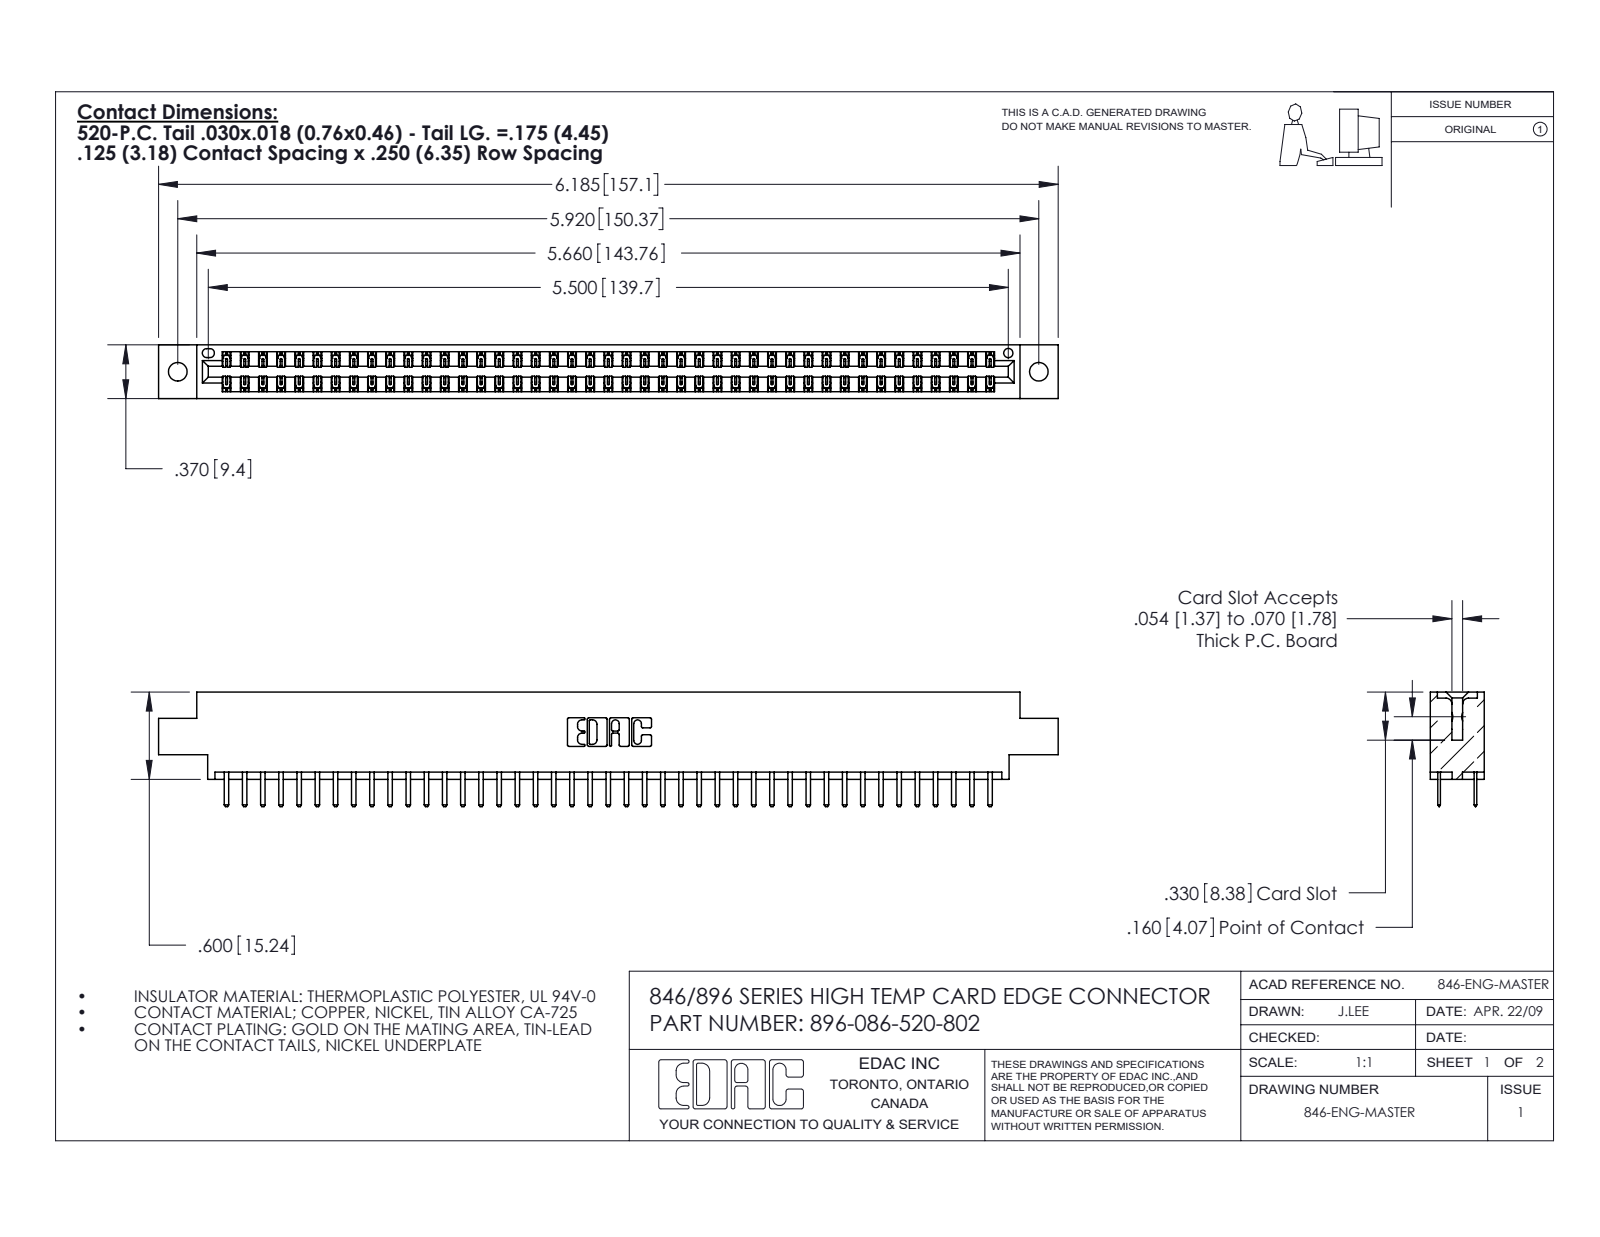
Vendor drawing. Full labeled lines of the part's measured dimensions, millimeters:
Part name (STEP PRODUCT): 345-292-001_345-293-120; 346 Part_0.170 Offset - 0.128 Dia; 396-086-520-802
STEP written by: SolidWorks 2016 (CONFIG_CONTROL_DESIGN)
Units: millimetres
Bodies: 87 solids, 4942 faces (3262 planar, 1680 cylindrical, 0 other)
Overall size (bounding box): 157.1 × 20 × 9.4
Volume: 15 100 mm³ · Surface area: 20 590 mm²
Round holes (diameter × count): ⌀3.3 ×2, ⌀1.6 ×1
Partial cylindrical surfaces — rounded edges, fillets, slot ends (radius × count): R0.2 ×129, R0.3 ×90, R0.3 ×22, R0.2 ×6, R0.8 ×6, R0.7 ×3, R0.4 ×2, R0.6 ×2
Main face-to-face distances: 1.2, 8.2, 6.4, 9.4, 7, 1.8, 7.6, 0.6, 3.8, 5.6
Hole centre spacings: 6.2, 145.1, 150.4
